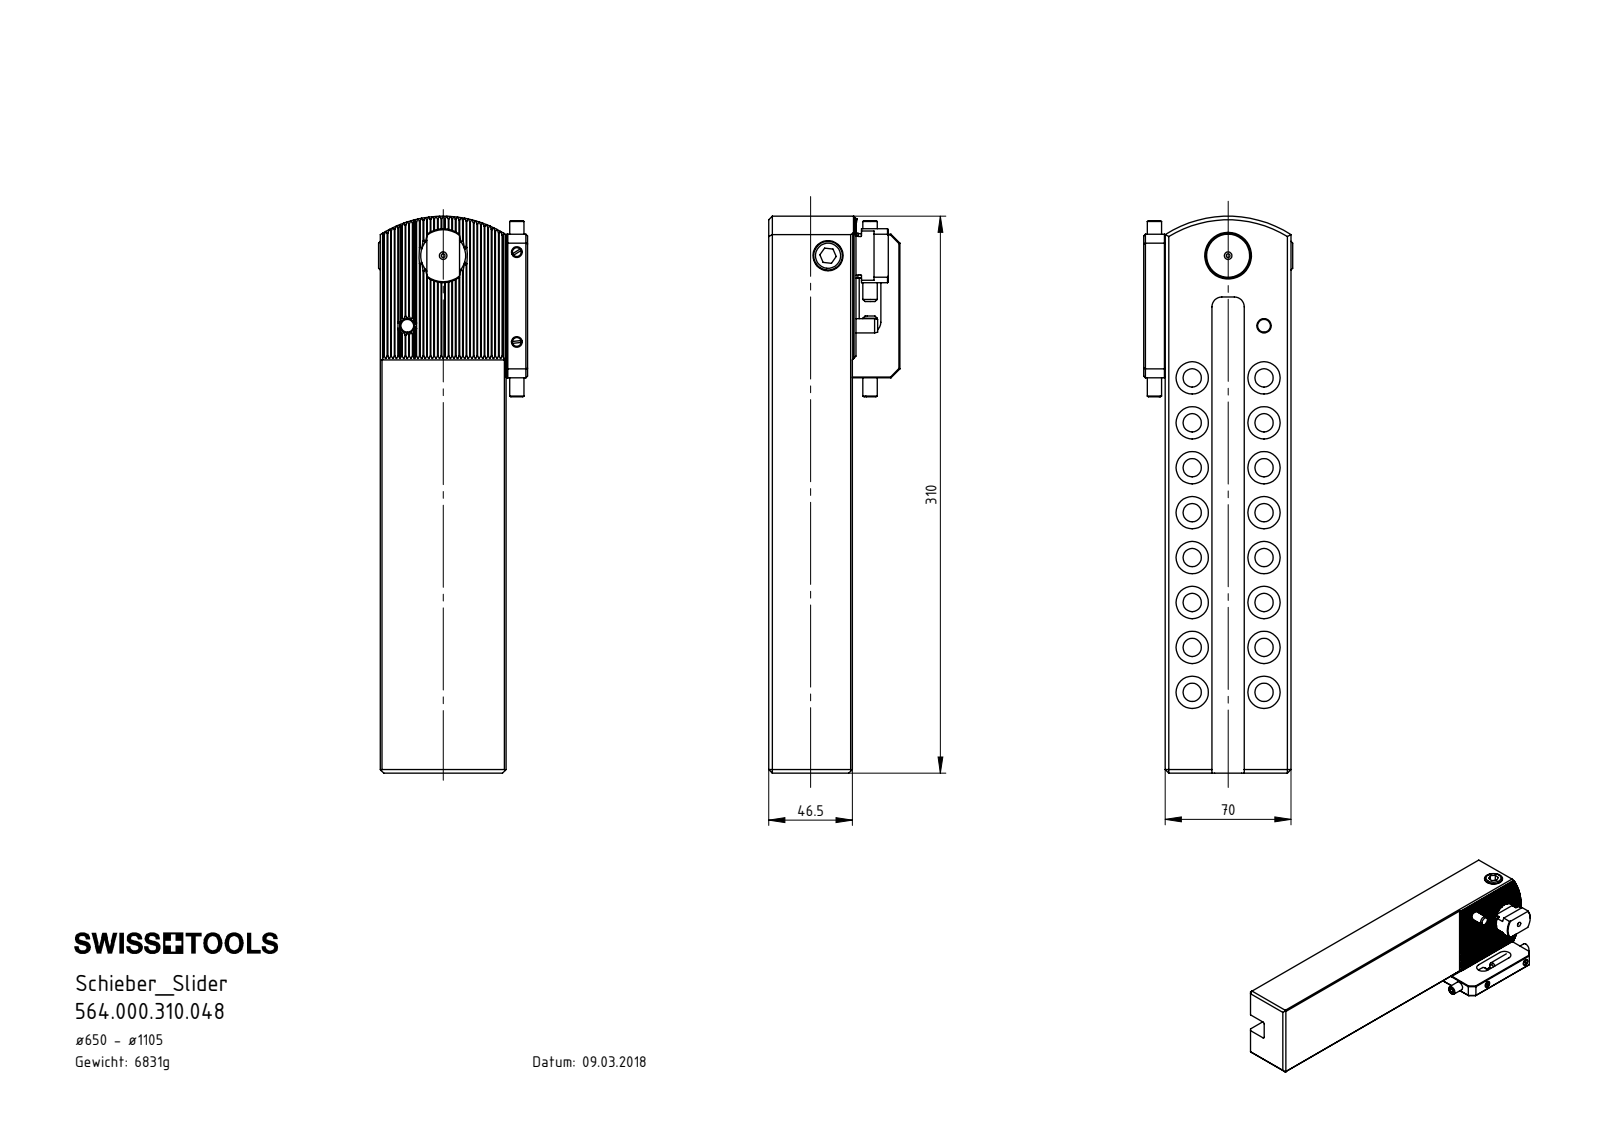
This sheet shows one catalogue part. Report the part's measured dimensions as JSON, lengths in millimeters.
{"part_name": "564.000.310.048; VK1-ER7.001.012; ISO 4766 - M6x12_ISO 4766 - M6 x 10; DIN 6912 - M10 x 12 (+8 more)", "step_written_by": "SolidWorks 2017 (CONFIG_CONTROL_DESIGN)", "units": "millimeters", "bodies": {"solids": 13, "faces": 695, "planar": 311, "cylindrical": 239, "other": 145}, "overall_size": [310, 83.5, 73], "volume_mm3": 870762, "surface_area_mm2": 143981, "round_holes": [[18, 17], [10.2, 16], [5, 2], [6, 2], [6.8, 2], [2, 1], [8, 1], [8.5, 1], [10.5, 1], [11, 1], [14, 1], [25, 1]], "round_bosses_or_shafts": [[16, 2], [6, 2], [10, 1]], "partial_cylinders_radius": [[0.14, 33], [2, 4], [1.5, 3], [5.5, 2], [6, 2], [12.3, 1], [15, 1], [65, 1]], "face_to_face_distances": [70, 46.5, 44, 26, 26.5, 18, 20, 12, 38, 56], "hole_center_spacings": [25, 47.17, 50, 64.03, 75, 85, 40, 100]}
